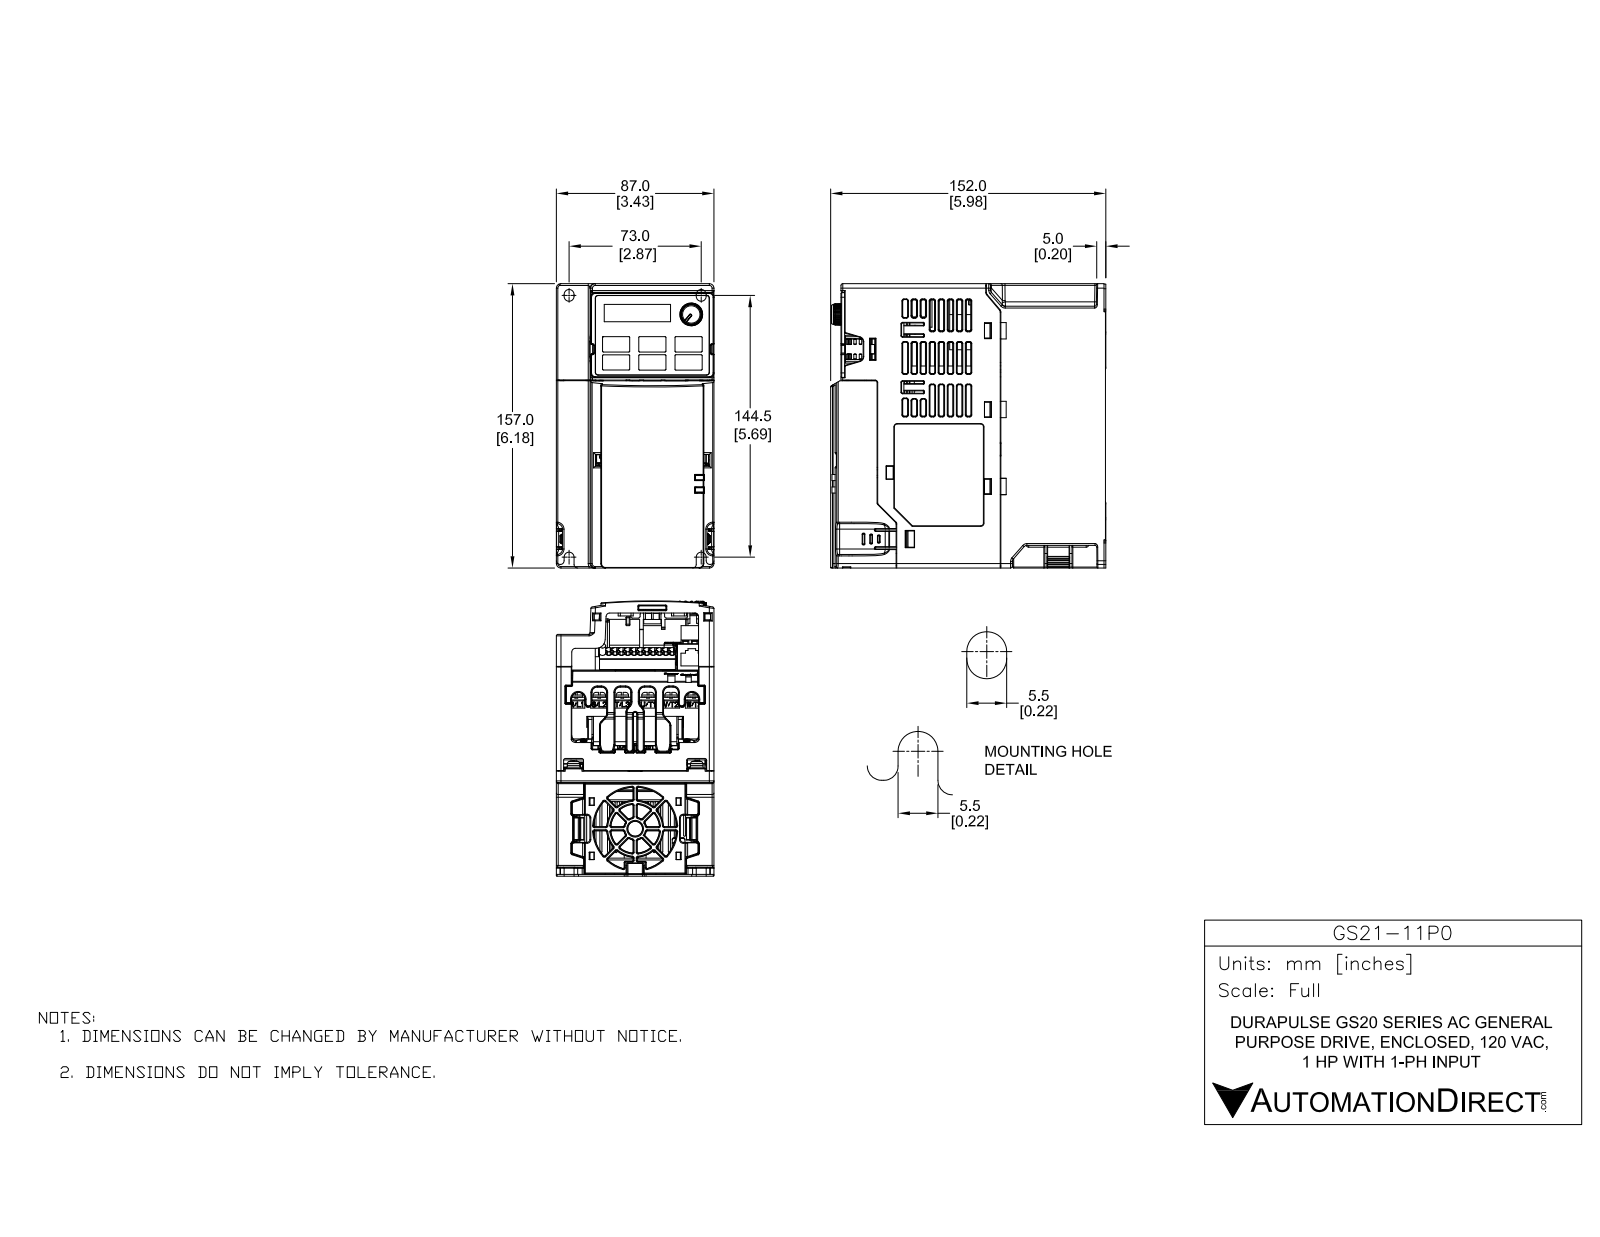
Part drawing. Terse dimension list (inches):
name: VFD-MS300-C1-PD-3D01 red 1c No Guard COMPLETE 1r1
written by: SolidWorks 2017 (AUTOMOTIVE_DESIGN)
unit: in
bodies: 41 solids, 5938 faces (3206 planar, 1722 cylindrical, 1010 other)
size: 6.193 × 5.984 × 3.484
volume: 17.03 in³; area: 354.3 in²
holes: 12× ⌀0.118, 10× ⌀0.169, 4× ⌀0.041, 4× ⌀0.045, 4× ⌀0.157, 2× ⌀0.11, 1× ⌀0.054, 1× ⌀0.058, 1× ⌀0.097, 1× ⌀0.429, 1× ⌀0.496
bosses: 12× ⌀0.039, 10× ⌀0.268, 10× ⌀0.157, 1× ⌀0.165, 1× ⌀0.157, 1× ⌀0.149, 1× ⌀0.018
rounds: 274× R0.02, 248× R0.012, 144× R0.039, 75× R0.031, 44× R0.079, 40× R0.008, 28× R0.028, 24× R0.016
face distances: 0.039, 3.425, 3.386, 0.098, 0.059, 0.354, 3.327, 3.287, 0.394, 3.346
hole spacings: 0.138, 0.276, 0.413, 0.551, 0.689, 0.827, 0.417, 0.965
